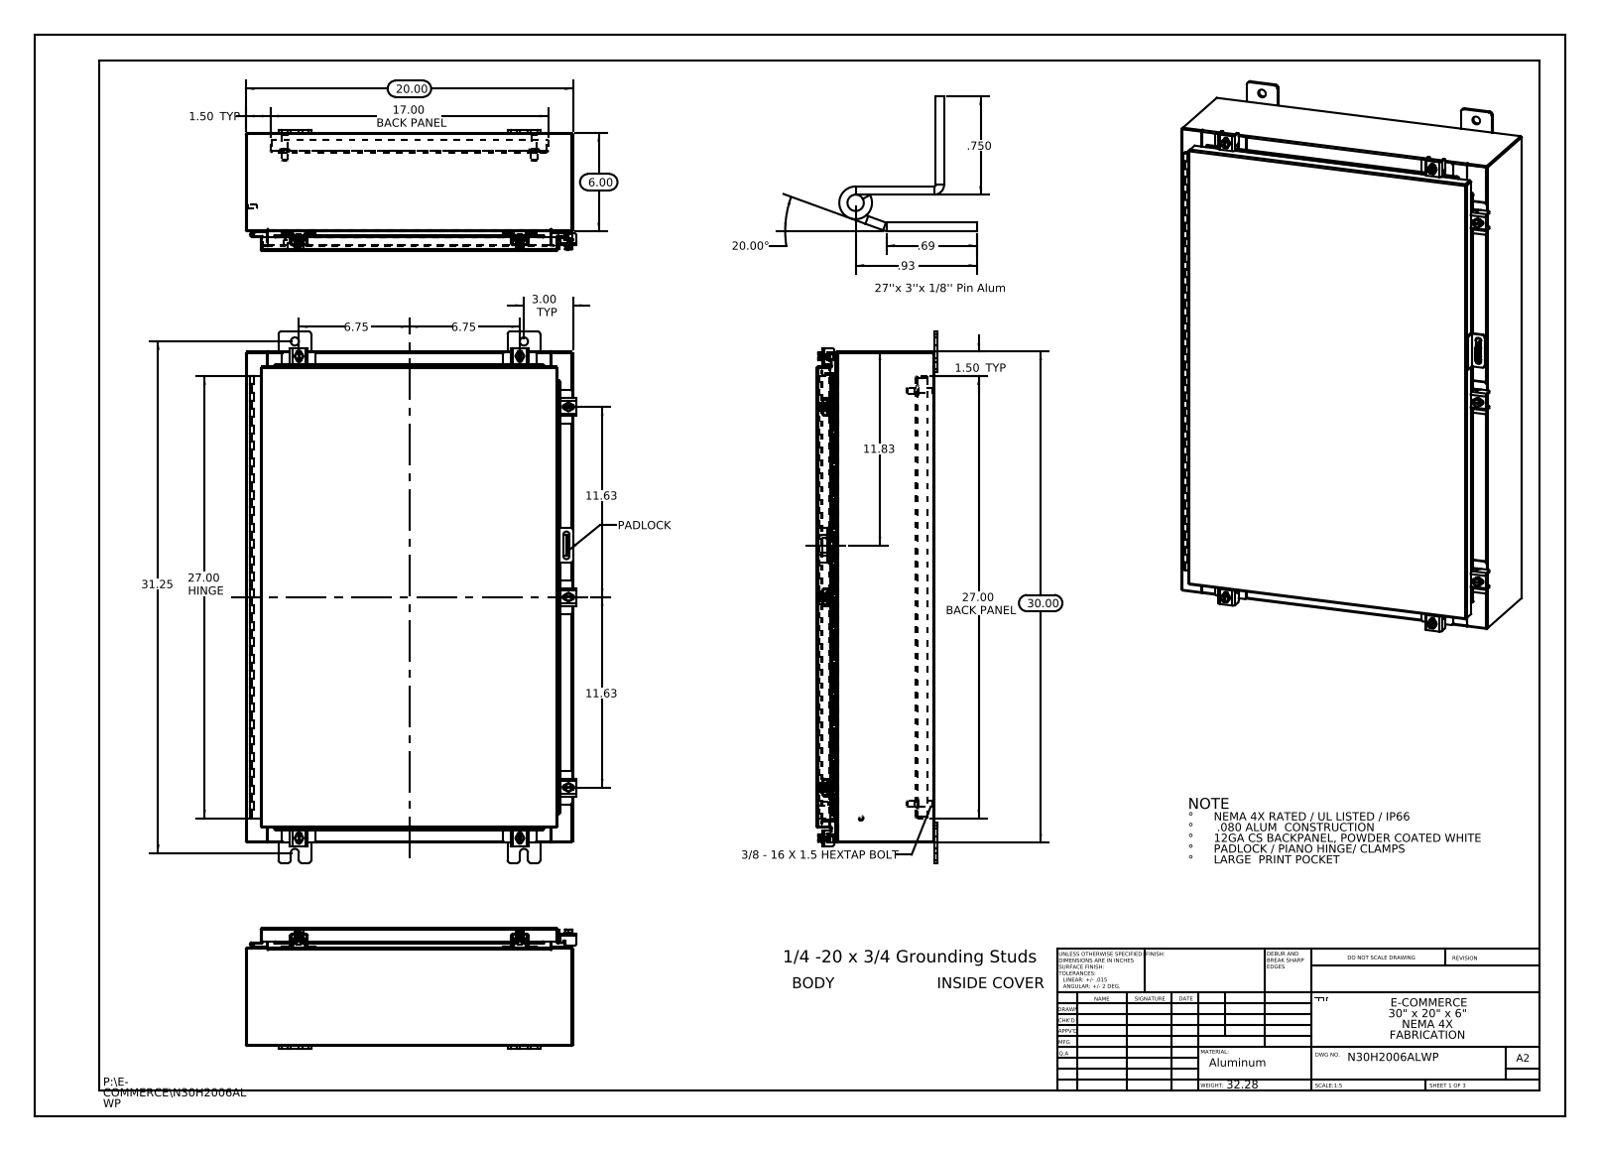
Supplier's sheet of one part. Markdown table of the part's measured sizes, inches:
| quantity | value |
| --- | --- |
| part name | N30H2006ALWP Padlock Hasp; N30H2006ALWP Mounting Feet; N30H2006ALWP Mounting Studs; N30H2006ALWP Hinge Enclosure Side2 (+8 more) |
| STEP written by | SolidWorks 2013 (CONFIG_CONTROL_DESIGN) |
| units | inches |
| bodies | 54 solids, 2016 faces (1062 planar, 838 cylindrical, 116 other) |
| overall size | 32.5 × 20.211 × 7.389 |
| volume | 214.2 in³ |
| surface area | 5 348 in² |
| round holes (diameter × count) | 0.5 × 8, 0.213 × 7, 0.26 × 7, 0.125 × 2, 0.125 × 1 |
| round bosses / shafts (diameter × count) | 0.25 × 8, 0.5 × 7, 0.399 × 7, 0.625 × 4, 0.375 × 4, 0.33 × 4, 0.315 × 2, 0.236 × 2 |
| partial cylindrical surfaces (radius × count) | 0.06 × 34, 0.013 × 27, 0.19 × 24, 0.088 × 21, 0.12 × 14, 0.141 × 14, 0.05 × 11, 0.08 × 10 |
| main face-to-face distances | 0.075, 7.126, 7.051, 7.201, 0.104, 1, 1.075, 6.051, 6.126, 1.179 |
| hole center spacings | 27.365, 30.898, 0.431, 0.934, 1.858, 2.275, 2.276, 2.327 |
